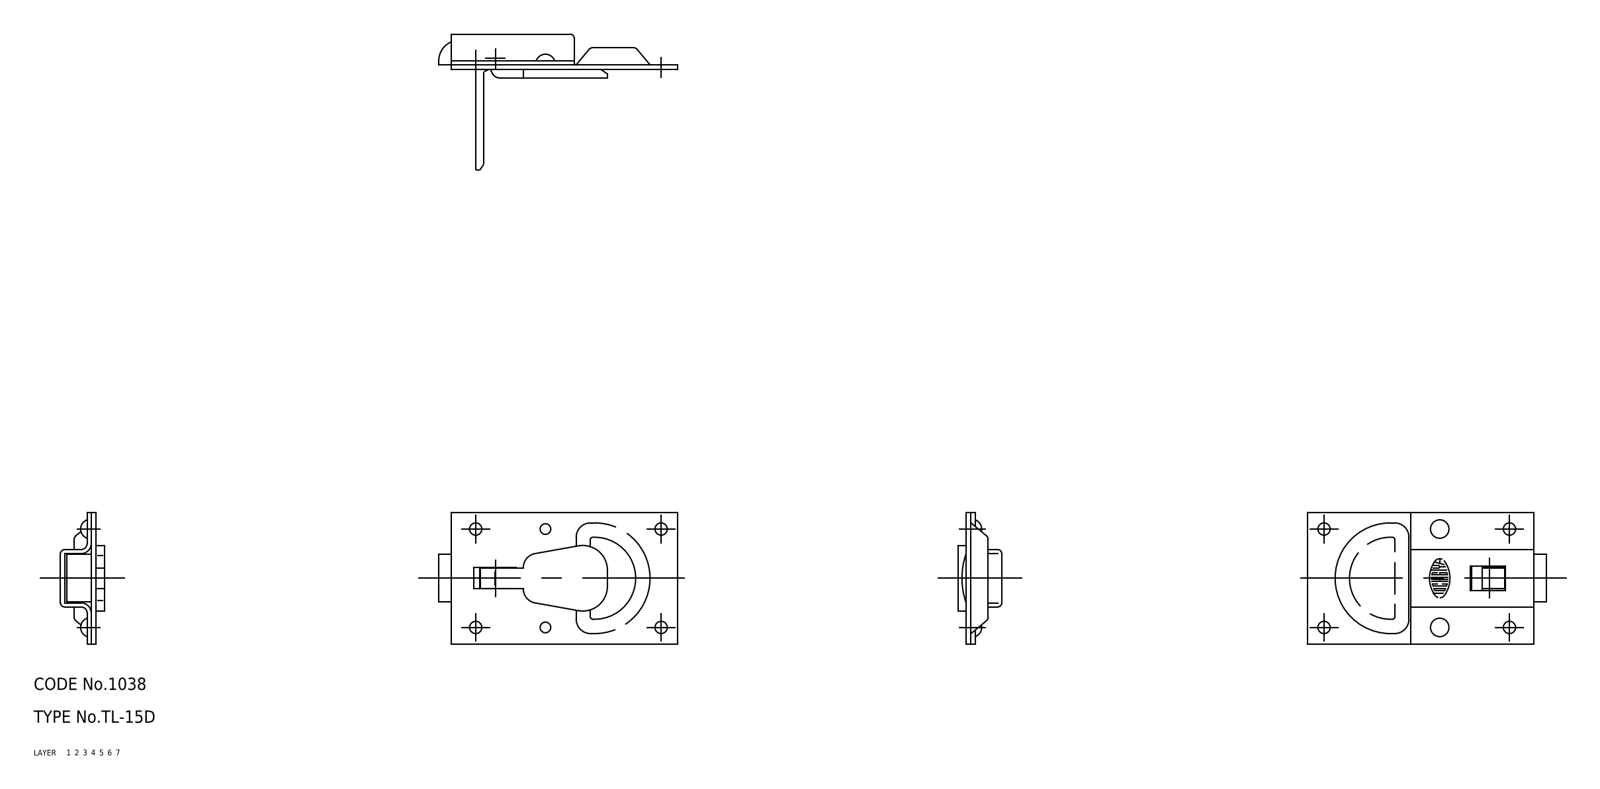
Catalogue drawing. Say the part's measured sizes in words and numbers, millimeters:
The part is named "rivet; shaft; lever; latch (+3 more)". Its 3-D file was written by "CADfix (AUTOMOTIVE_DESIGN)". It is 7 solids with 163 faces: 0 planar, 0 cylindrical and 163 other. Overall it measures 58.2 by 32 by 10.7 millimeters. Its volume is 5 021 cubic millimeters and its surface area 8 646 square millimeters.
